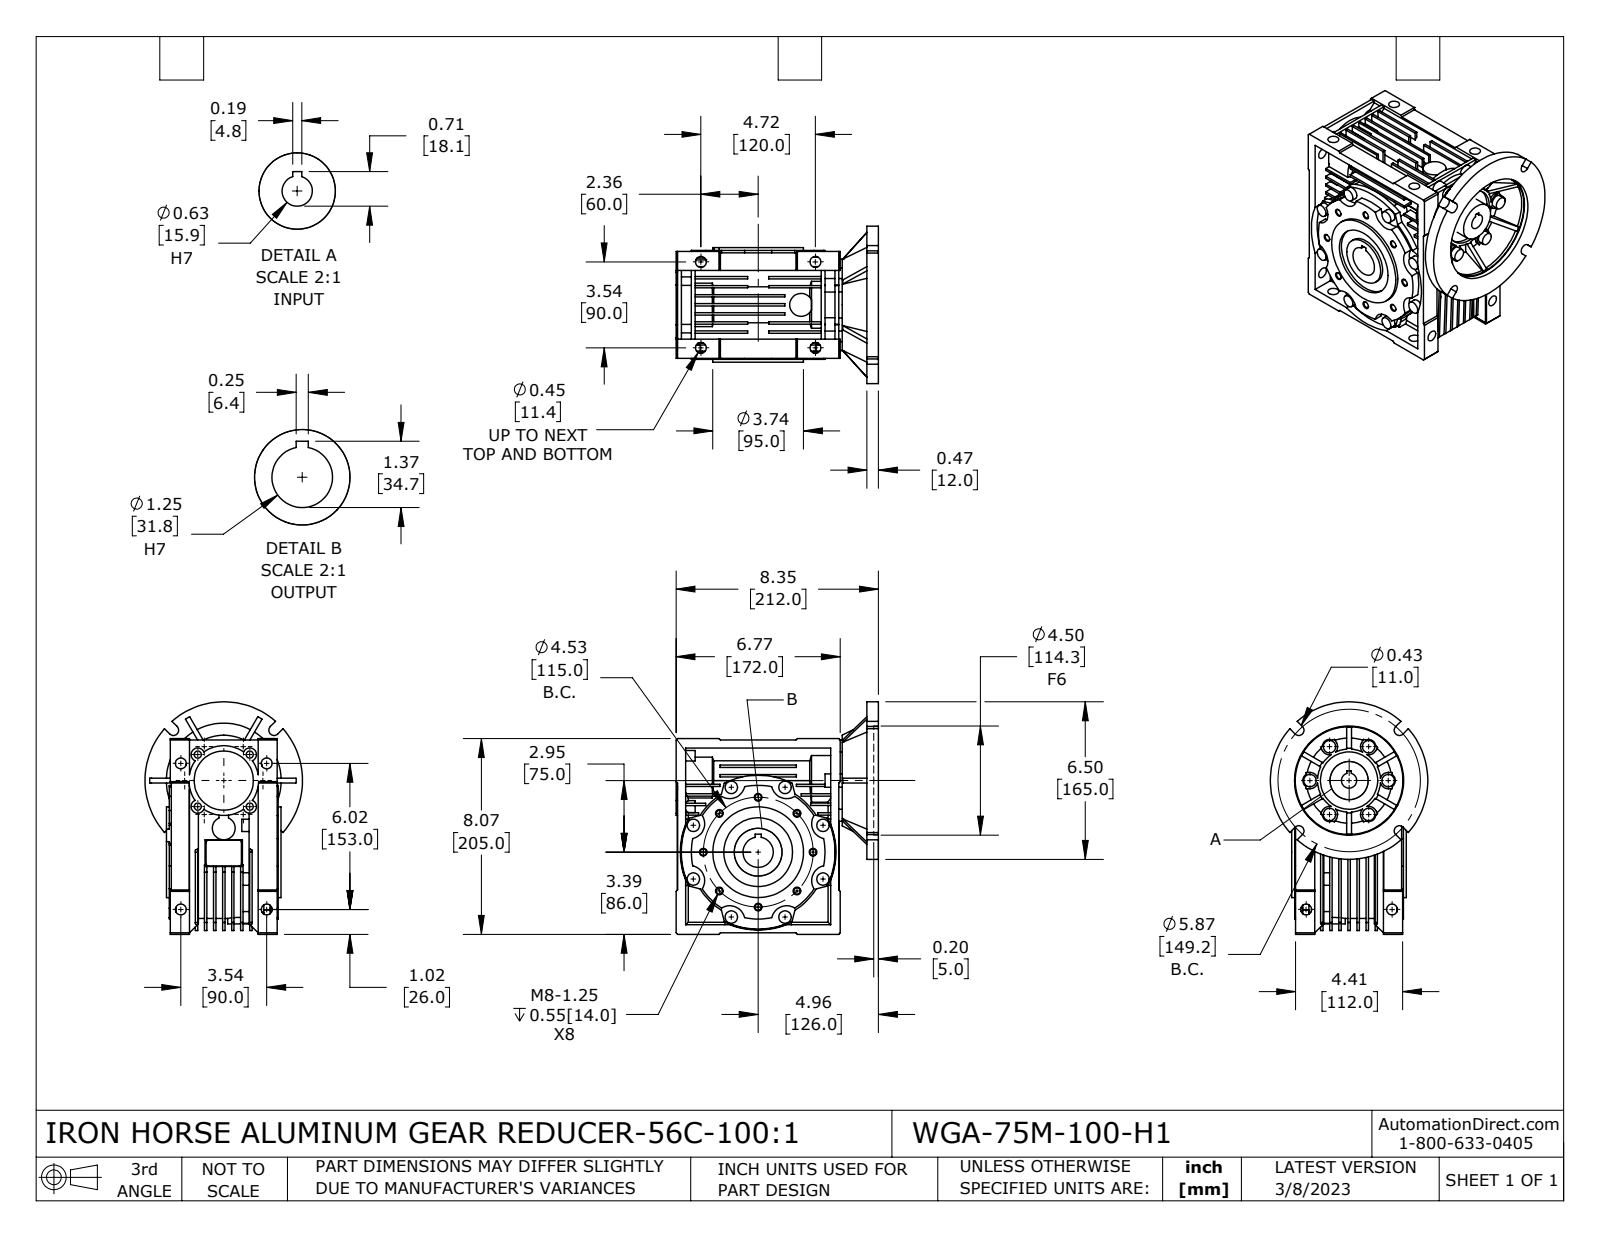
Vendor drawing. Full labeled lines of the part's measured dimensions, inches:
Part name (STEP PRODUCT): WGA-75M-100-H1
STEP written by: SolidWorks 2021 (CONFIG_CONTROL_DESIGN)
Units: inches
Bodies: 4 solids, 1179 faces (675 planar, 386 cylindrical, 118 other)
Overall size (bounding box): 9.587 × 8.346 × 6.496
Volume: 180.8 in³ · Surface area: 779.6 in²
Round holes (diameter × count): ⌀0.262 ×8, ⌀0.448 ×8, ⌀0.293 ×4, ⌀0.625 ×1, ⌀0.65 ×1, ⌀1 ×1, ⌀1.25 ×1, ⌀1.535 ×1, ⌀1.654 ×1, ⌀1.969 ×1, ⌀2.441 ×1, ⌀2.677 ×1
Round bosses / shafts (diameter × count): ⌀0.512 ×14, ⌀0.945 ×3, ⌀6.496 ×1, ⌀5.509 ×1, ⌀5.465 ×1, ⌀3.74 ×1, ⌀2.992 ×1, ⌀2.795 ×1
Partial cylindrical surfaces — rounded edges, fillets, slot ends (radius × count): R0.276 ×10, R0.63 ×8, R0.295 ×6, R0.335 ×6, R0.098 ×4, R0.217 ×4, R1.299 ×1, R1.417 ×1
Main face-to-face distances: 0.374, 0.098, 0.472, 0.748, 0.276, 1.122, 1.496, 0.394, 0.65, 0.846
Hole centre spacings: 2.264, 1.733, 3.202, 4.183, 1.515, 2.143, 3.543, 4.528
